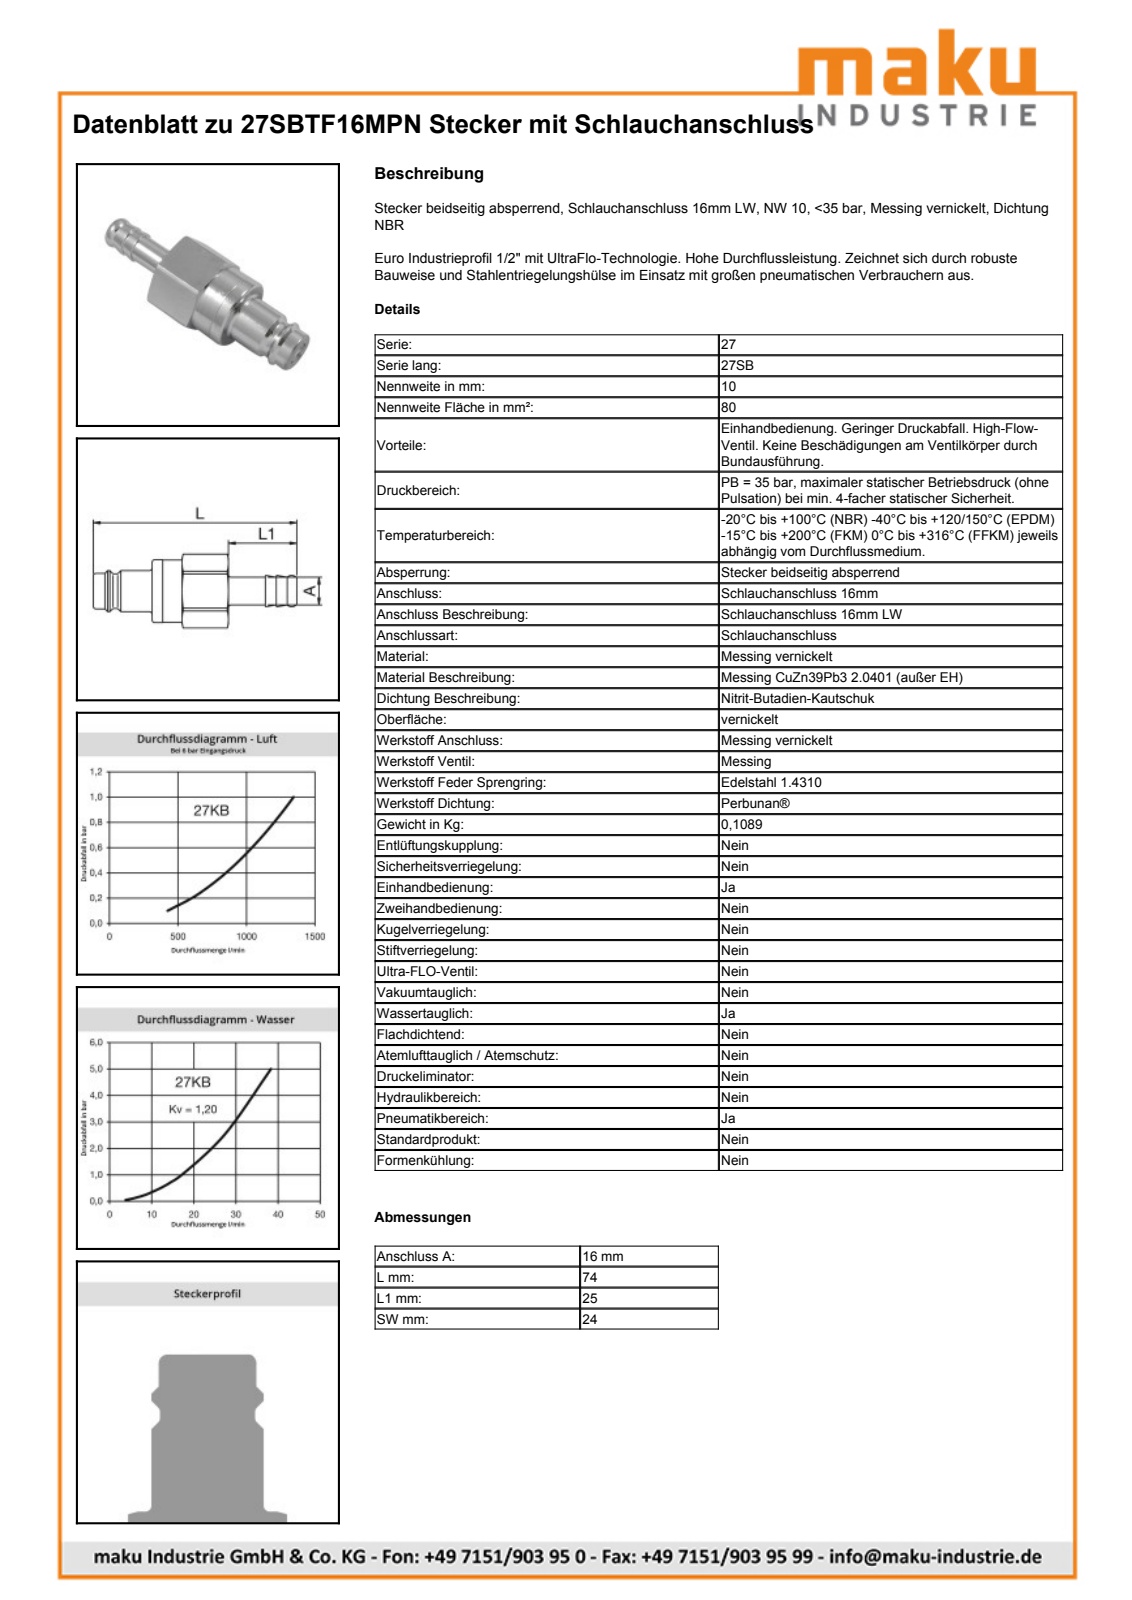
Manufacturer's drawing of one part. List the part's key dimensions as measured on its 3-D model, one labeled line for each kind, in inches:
Part name (STEP PRODUCT): D105157
STEP written by: Autodesk Inventor 2011 (AUTOMOTIVE_DESIGN)
Units: inches
Bodies: 1 solid, 70 faces (16 planar, 20 cylindrical, 34 other)
Overall size (bounding box): 2.929 × 1.045 × 1.035
Volume: 1.238 in³ · Surface area: 11.67 in²
Round holes (diameter × count): ⌀0.709 ×1, ⌀0.748 ×1, ⌀0.799 ×1
Round bosses / shafts (diameter × count): ⌀0.906 ×1, ⌀0.896 ×1, ⌀0.728 ×1, ⌀0.634 ×1, ⌀0.591 ×1, ⌀0.557 ×1, ⌀0.512 ×1, ⌀0.498 ×1
Partial cylindrical surfaces — rounded edges, fillets, slot ends (radius × count): R0.533 ×1
Main face-to-face distances: 0.945, 0.944, 0.984, 1.098, 2.083, 0.846, 1.945, 2.929, 1.238, 1
